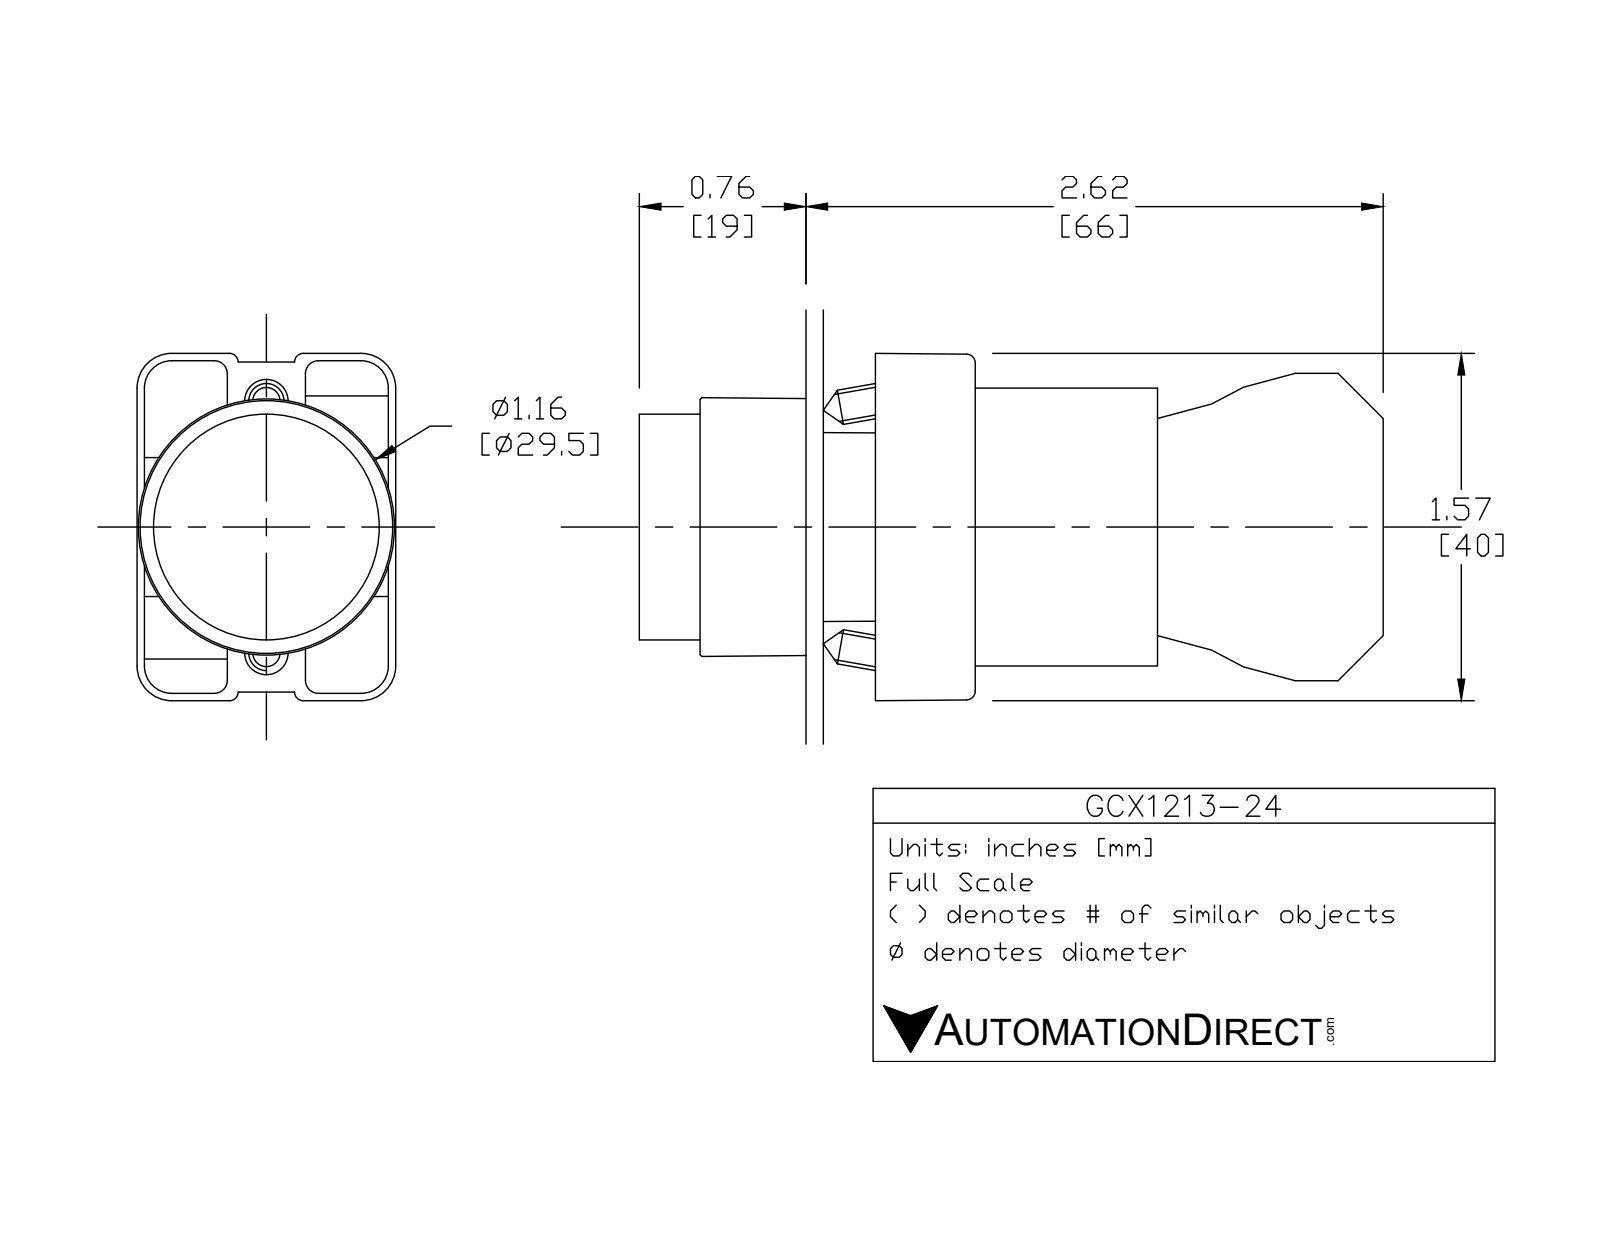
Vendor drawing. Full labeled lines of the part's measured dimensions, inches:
Part name (STEP PRODUCT): ecx1029; GCX1213-24; ecx1040; ECX1050 (+1 more)
STEP written by: SolidWorks 2016 (AUTOMOTIVE_DESIGN)
Units: inches
Bodies: 7 solids, 425 faces (250 planar, 144 cylindrical, 31 other)
Overall size (bounding box): 3.319 × 1.581 × 1.177
Volume: 2.721 in³ · Surface area: 36.32 in²
Round holes (diameter × count): ⌀0.079 ×2, ⌀0.124 ×2, ⌀0.13 ×2, ⌀0.087 ×1, ⌀0.197 ×1, ⌀0.469 ×1, ⌀0.878 ×1, ⌀0.888 ×1, ⌀1.024 ×1
Round bosses / shafts (diameter × count): ⌀0.157 ×4, ⌀1.175 ×1, ⌀1.004 ×1, ⌀0.945 ×1, ⌀0.856 ×1, ⌀0.78 ×1, ⌀0.504 ×1
Partial cylindrical surfaces — rounded edges, fillets, slot ends (radius × count): R0.059 ×24, R0.041 ×12, R0.124 ×12, R0.157 ×12, R0.039 ×8, R0.128 ×2, R0.02 ×1, R0.063 ×1
Main face-to-face distances: 0.827, 0.579, 1.171, 2.02, 1.193, 0.031, 0.033, 0.573, 1.165, 0.593
Hole centre spacings: 0.236, 0.544, 0.472, 0.49
